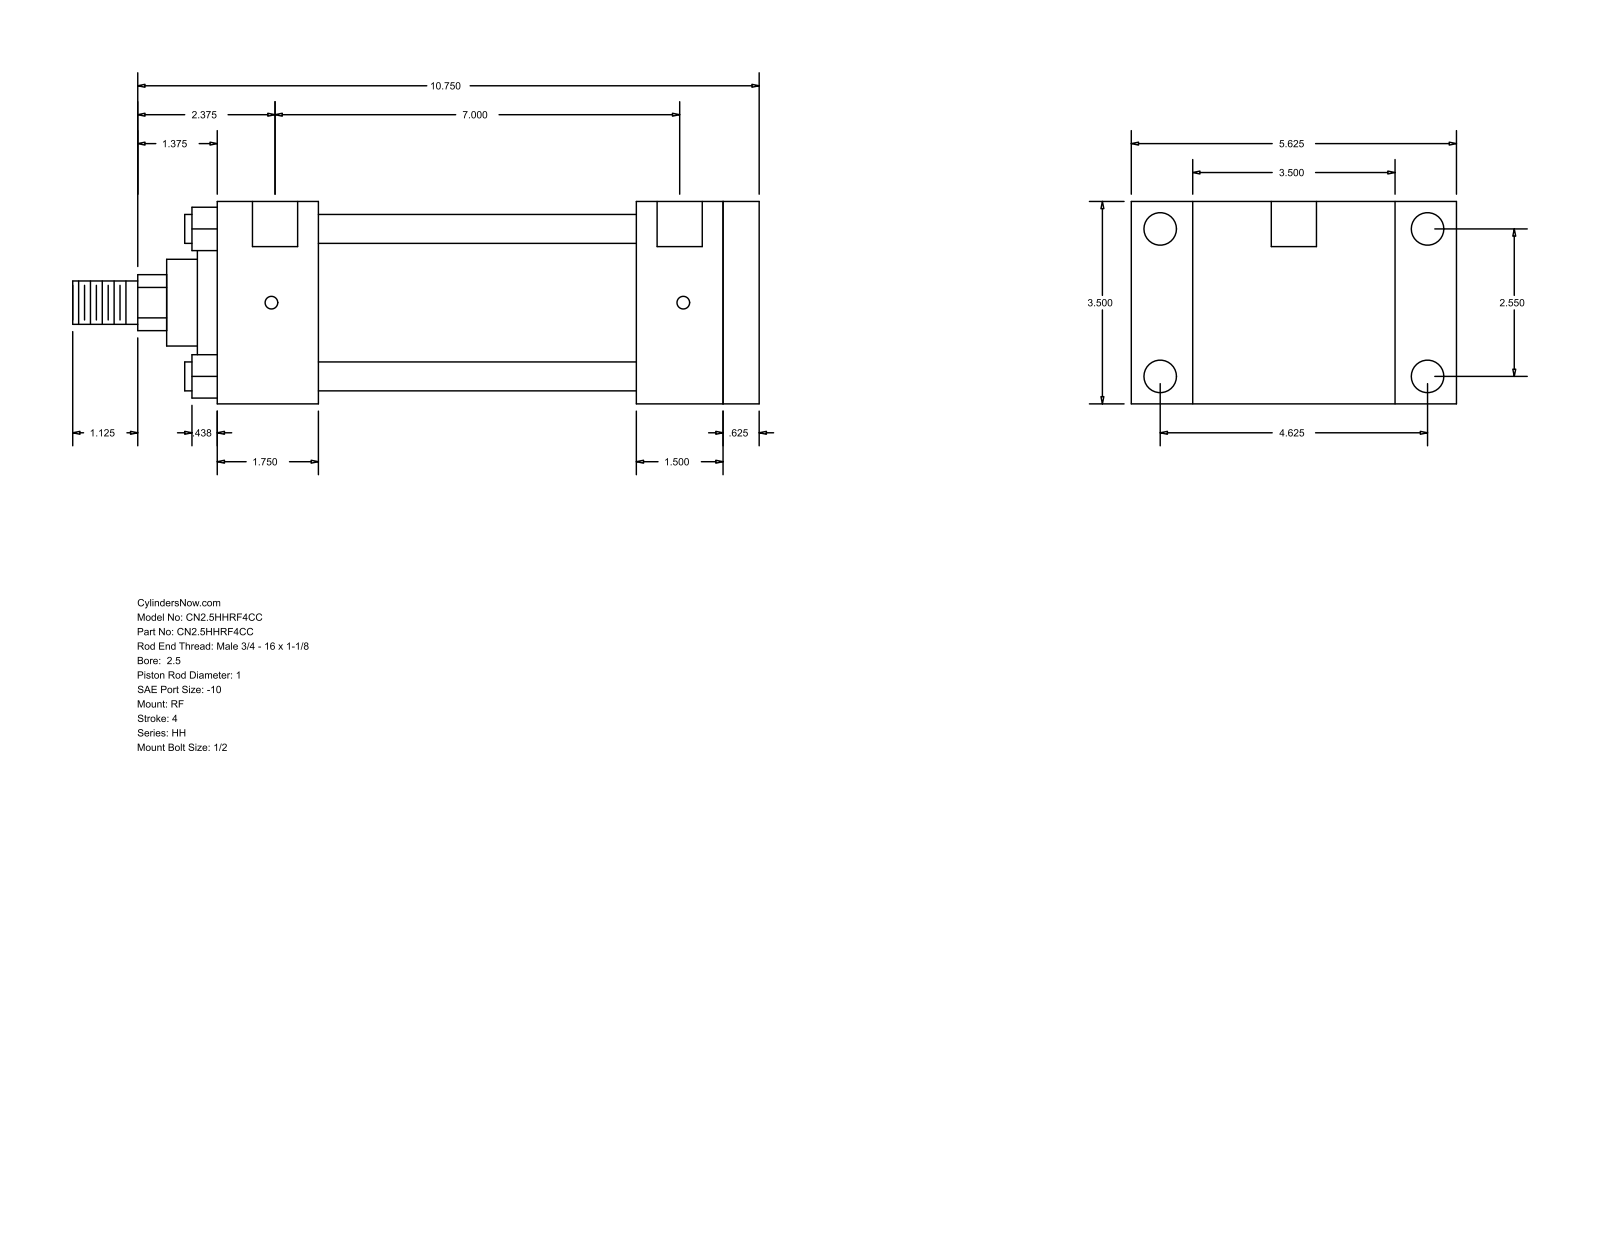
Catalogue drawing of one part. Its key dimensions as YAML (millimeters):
part_name: "HH_RF__0250_1"
step_written_by: "GSSL Pune (CONFIG_CONTROL_DESIGN)"
units: millimeters
bodies: {solids: 0, faces: 94, planar: 65, cylindrical: 29, other: 0}
overall_size: [301.62, 142.88, 88.9]
round_holes:
  - {diameter: 5.56, count: 4}
  - {diameter: 14.3, count: 4}
  - {diameter: 19.84, count: 2}
round_bosses_or_shafts:
  - {diameter: 12.7, count: 4}
  - {diameter: 73.03, count: 1}
  - {diameter: 60.33, count: 1}
  - {diameter: 38.1, count: 1}
  - {diameter: 25.4, count: 1}
  - {diameter: 19.05, count: 1}
partial_cylinders:
  - {radius: 12.29, count: 1}
face_to_face_distances: [88.9, 15.87, 222.26, 238.13, 44.46, 177.8, 193.67, 184.15, 139.69, 38.11]
hole_center_spacings: [1.59, 64.76, 117.48, 134.15, 179.38, 180.97, 177.79]
